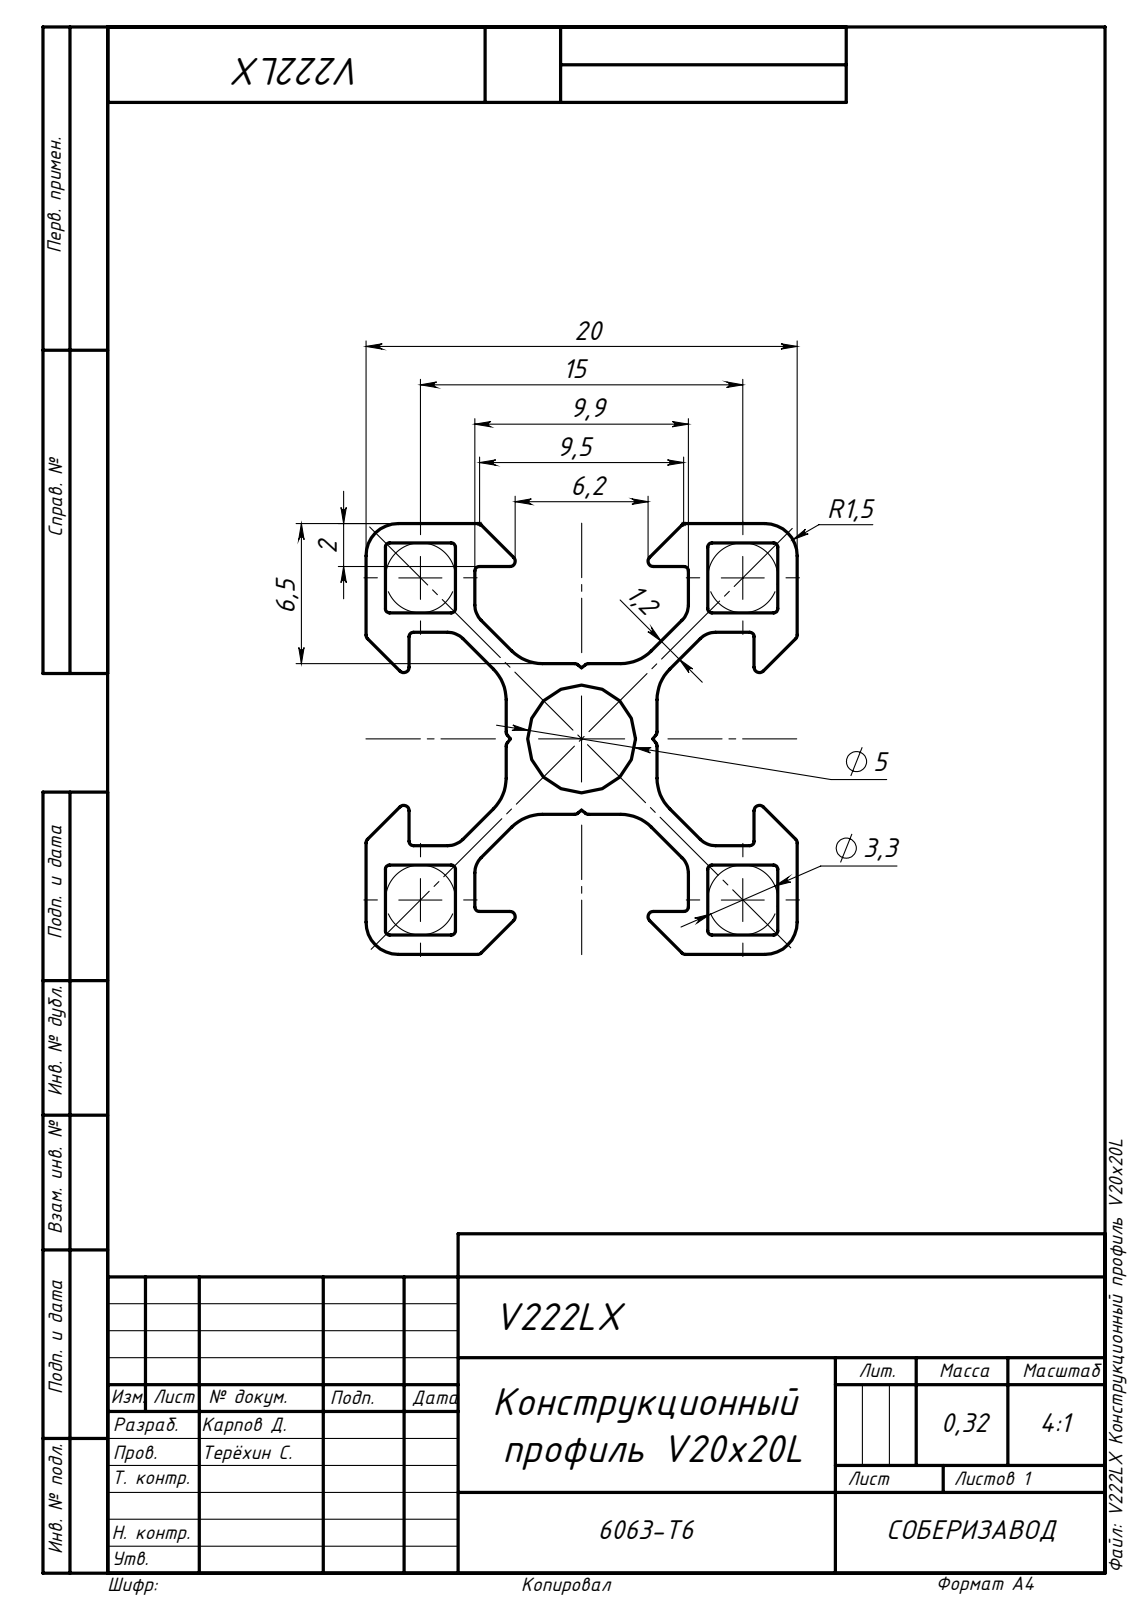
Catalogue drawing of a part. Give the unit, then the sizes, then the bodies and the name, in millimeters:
Units: millimetres
Overall size (bounding box): 1000 × 20 × 20
Round holes (diameter × count): ⌀5 ×1
Partial cylindrical surfaces — rounded edges, fillets, slot ends (radius × count): R0.2 ×24, R0.25 ×24, R1 ×8, R2 ×8, R1.5 ×4
Main face-to-face distances: 4.15, 0.9, 14.95, 15.85, 19.1, 3.25, 3.13, 4.33, 20, 5.05
Volume: 119 724 mm³ · Surface area: 205 189 mm²
Bodies: 1 solid, 146 faces (74 planar, 72 cylindrical, 0 other)
STEP written by: SolidWorks 2019 (AUTOMOTIVE_DESIGN)
